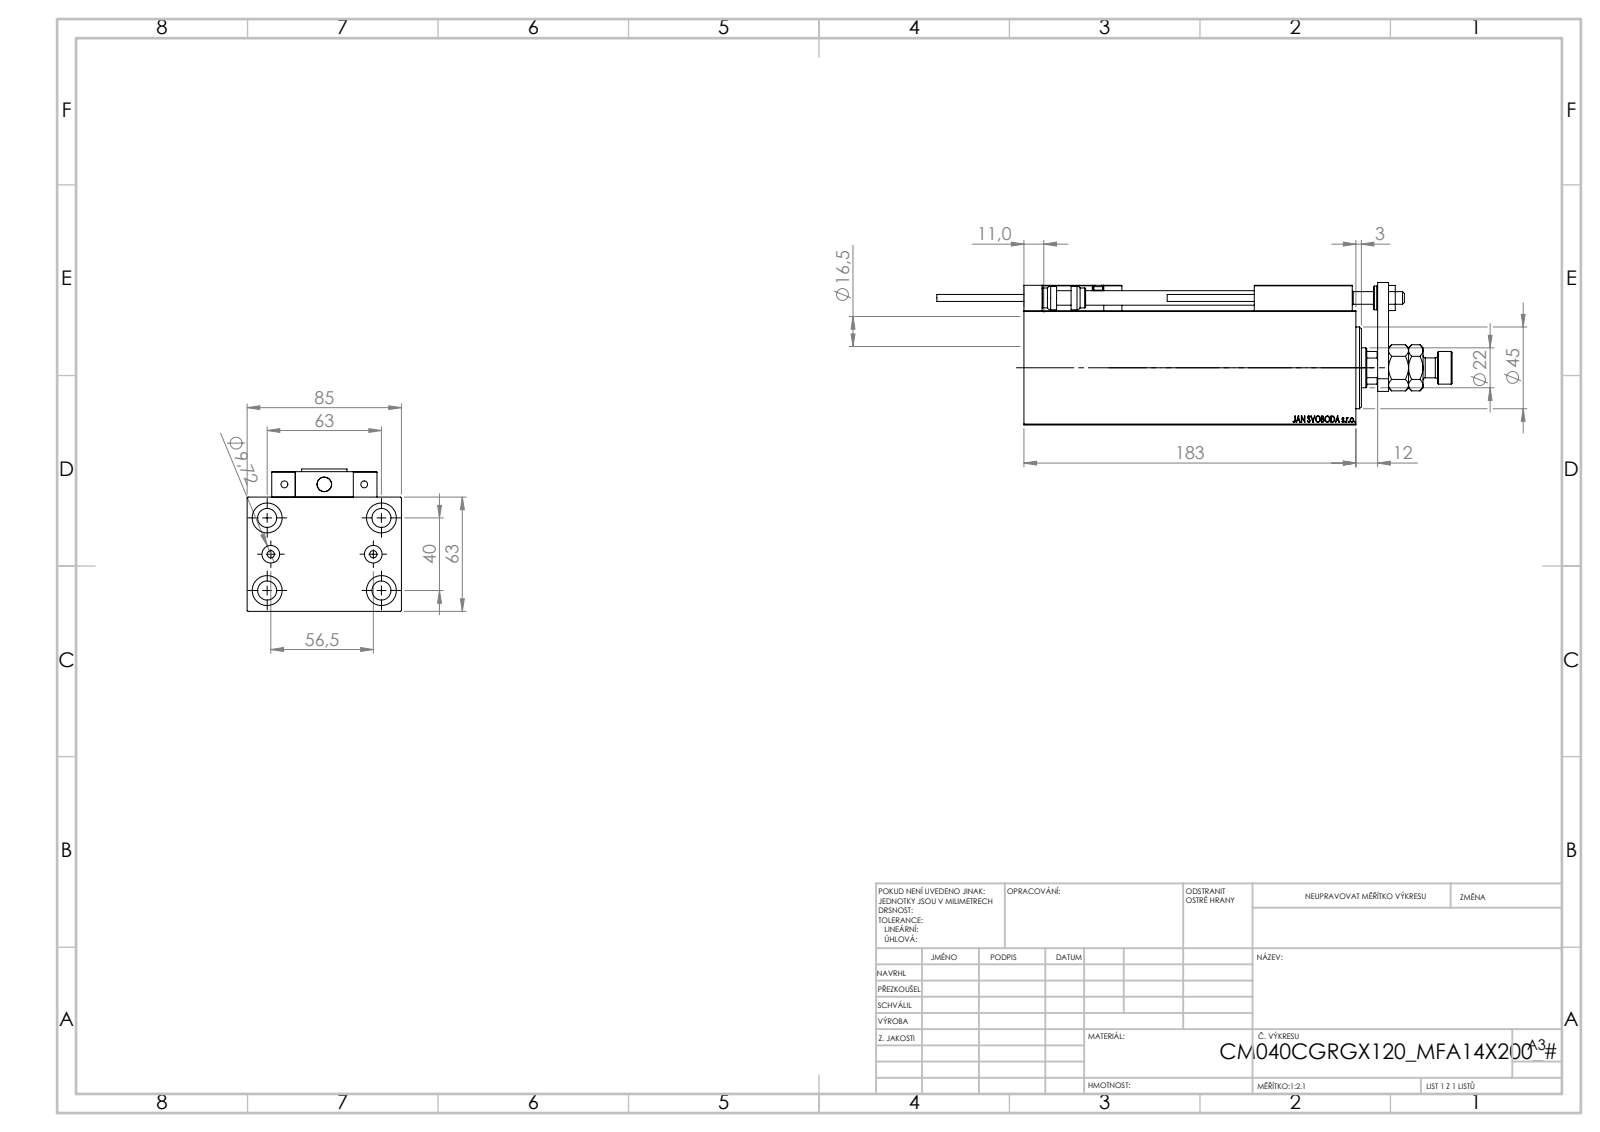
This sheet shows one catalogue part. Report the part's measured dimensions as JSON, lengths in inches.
{"part_name": "NUT_D12; ALLEN BOLT D8; ZARAZKA; TYC_L79 (+7 more)", "step_written_by": "SolidWorks 2019 (CONFIG_CONTROL_DESIGN)", "units": "inches", "bodies": {"solids": 24, "faces": 1330, "planar": 576, "cylindrical": 188, "other": 566}, "overall_size": [11.181, 3.346, 3.091], "volume_in3": 52.69, "surface_area_in2": 263.6, "round_holes": [[0.157, 6], [0.315, 5], [0.65, 5], [0.126, 4], [0.413, 4], [0.197, 2], [0.383, 2], [0.276, 1], [0.492, 1], [0.866, 1], [1.004, 1], [1.575, 1]], "round_bosses_or_shafts": [[0.433, 2], [0.197, 2], [0.15, 2], [0.709, 1], [0.512, 1]], "partial_cylinders_radius": [[0.012, 30], [0.118, 2], [0.413, 1]], "face_to_face_distances": [2.48, 3.346, 0.472, 6.732, 7.205, 0.551, 0.709, 1.181, 3.031, 0.787], "hole_center_spacings": [1.469, 0.448, 0.787, 0.791, 0.807, 1.165, 1.169, 1.42]}
